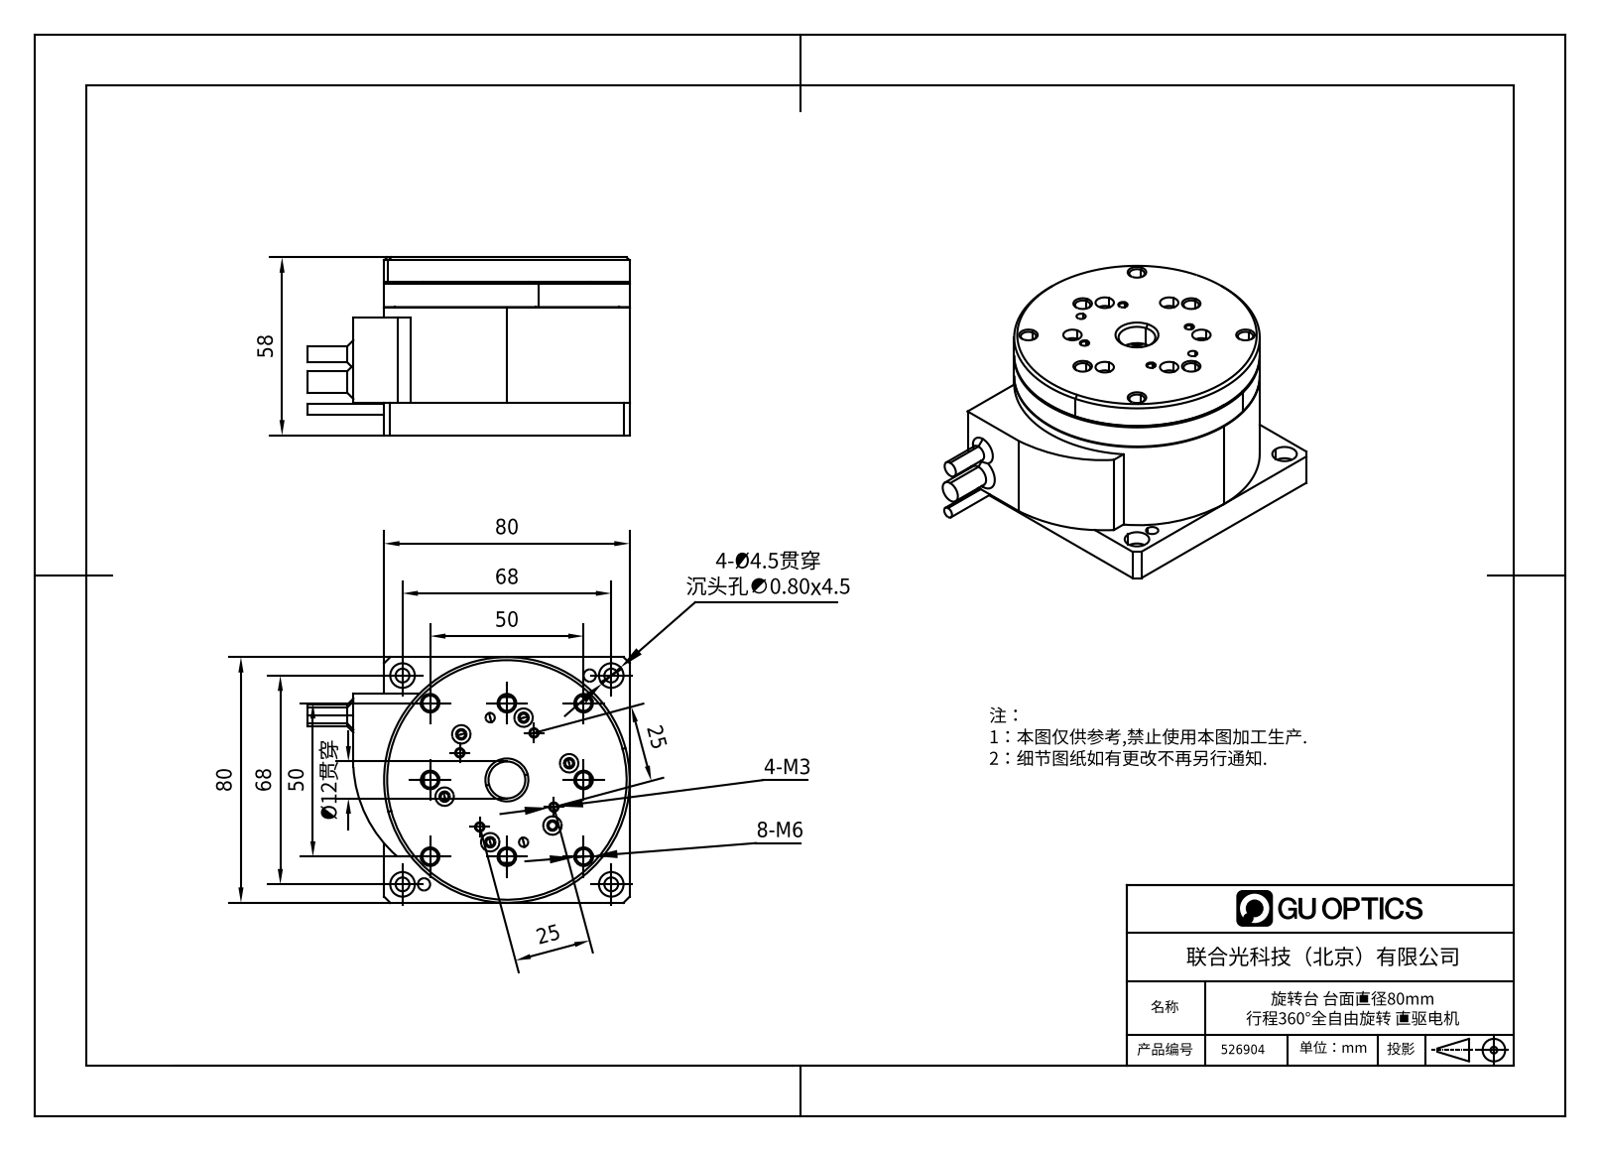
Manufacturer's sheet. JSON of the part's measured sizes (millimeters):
{"part_name": "FMSR80D", "step_written_by": "SolidWorks 2017 (AUTOMOTIVE_DESIGN)", "units": "millimeters", "bodies": {"solids": 3, "faces": 499, "planar": 241, "cylindrical": 206, "other": 52}, "overall_size": [105, 80, 58], "volume_mm3": 307232, "surface_area_mm2": 63226, "round_holes": [[6, 24], [2.5, 10], [5, 8], [3.4, 6], [4.5, 4], [6.7, 4], [8, 4], [3, 2], [4, 2], [12, 1], [12.05, 1], [30, 1]], "round_bosses_or_shafts": [[5.5, 18], [80, 1], [73, 1], [54, 1], [29.99, 1], [7, 1], [5.2, 1], [3.6, 1]], "partial_cylinders_radius": [[1.85, 1], [41.56, 1]], "face_to_face_distances": [50, 38.5, 8, 11.5, 58, 19.5, 38.9, 0.4, 11.1, 19.1], "hole_center_spacings": [30.75, 51.32, 53.26, 21, 41.48, 15.92, 20.03, 34.15]}
